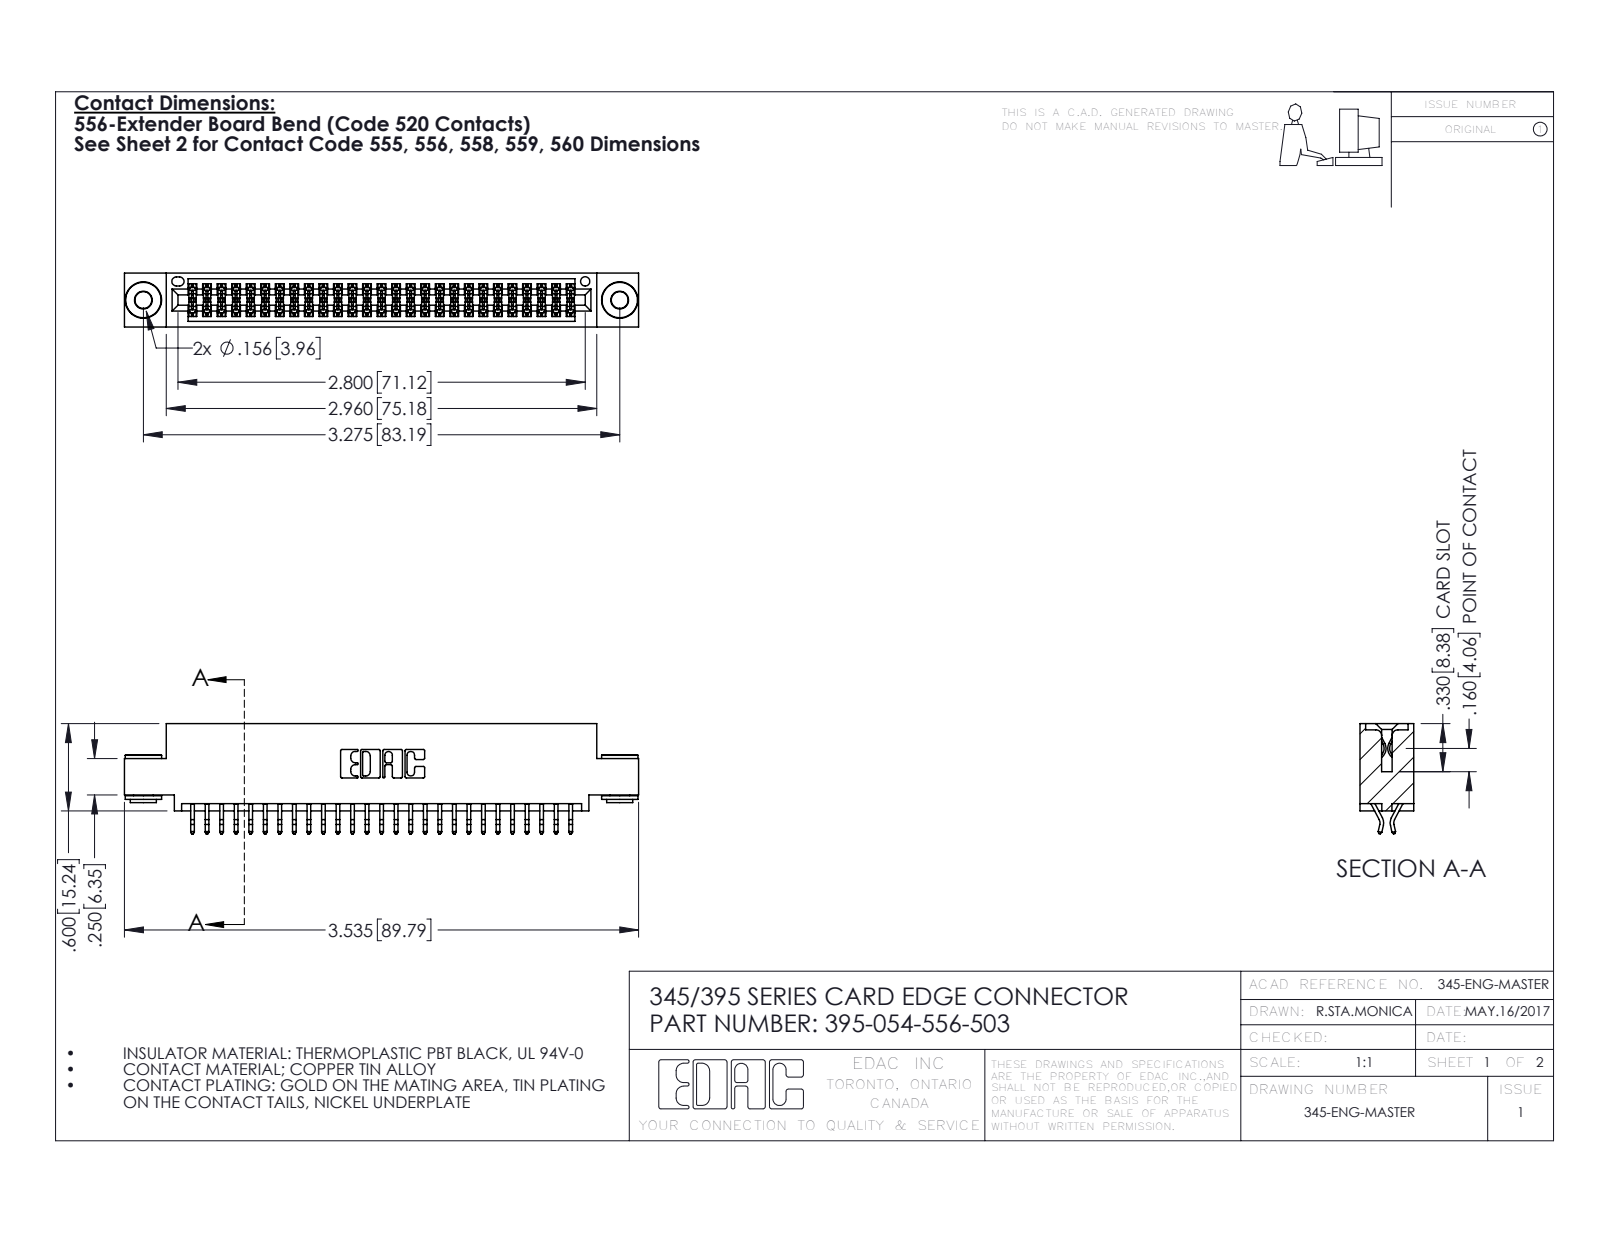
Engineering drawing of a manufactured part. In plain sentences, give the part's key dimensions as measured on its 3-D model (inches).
The part is named "345 Part_0.110 Offset - 0.156 Dia-TH; 345-292-001_556 Tail; 345-250-002_345-250-002-102; 395-054-556-503". Its 3-D file was written by "SolidWorks 2016 (CONFIG_CONTROL_DESIGN)". It is 57 solids with 3192 faces: 2092 planar, 1092 cylindrical and 8 other. Overall it measures 3.535 by 0.757 by 0.37 inches. Its volume is 0.52 cubic inches and its surface area 19.47 square inches. Round holes: 2 of diameter 0.116, 2 of diameter 0.156, 1 of diameter 0.064. Round bosses or shafts: 2 of diameter 0.25, 2 of diameter 0.18, 2 of diameter 0.136. Partial cylindrical surfaces (rounded edges, fillets, slot ends): 81 of radius 0.006, 22 of radius 0.01, 6 of radius 0.007, 6 of radius 0.031, 3 of radius 0.026, 2 of radius 0.01, 2 of radius 0.014, 2 of radius 0.019. The main face-to-face distances are 0.072, 0.298, 0.37, 0.2, 0.025, 0.098, 0.272, 0.225, 0.175, 0.149. The hole center spacings are 0.27, 3.04, 3.275.
